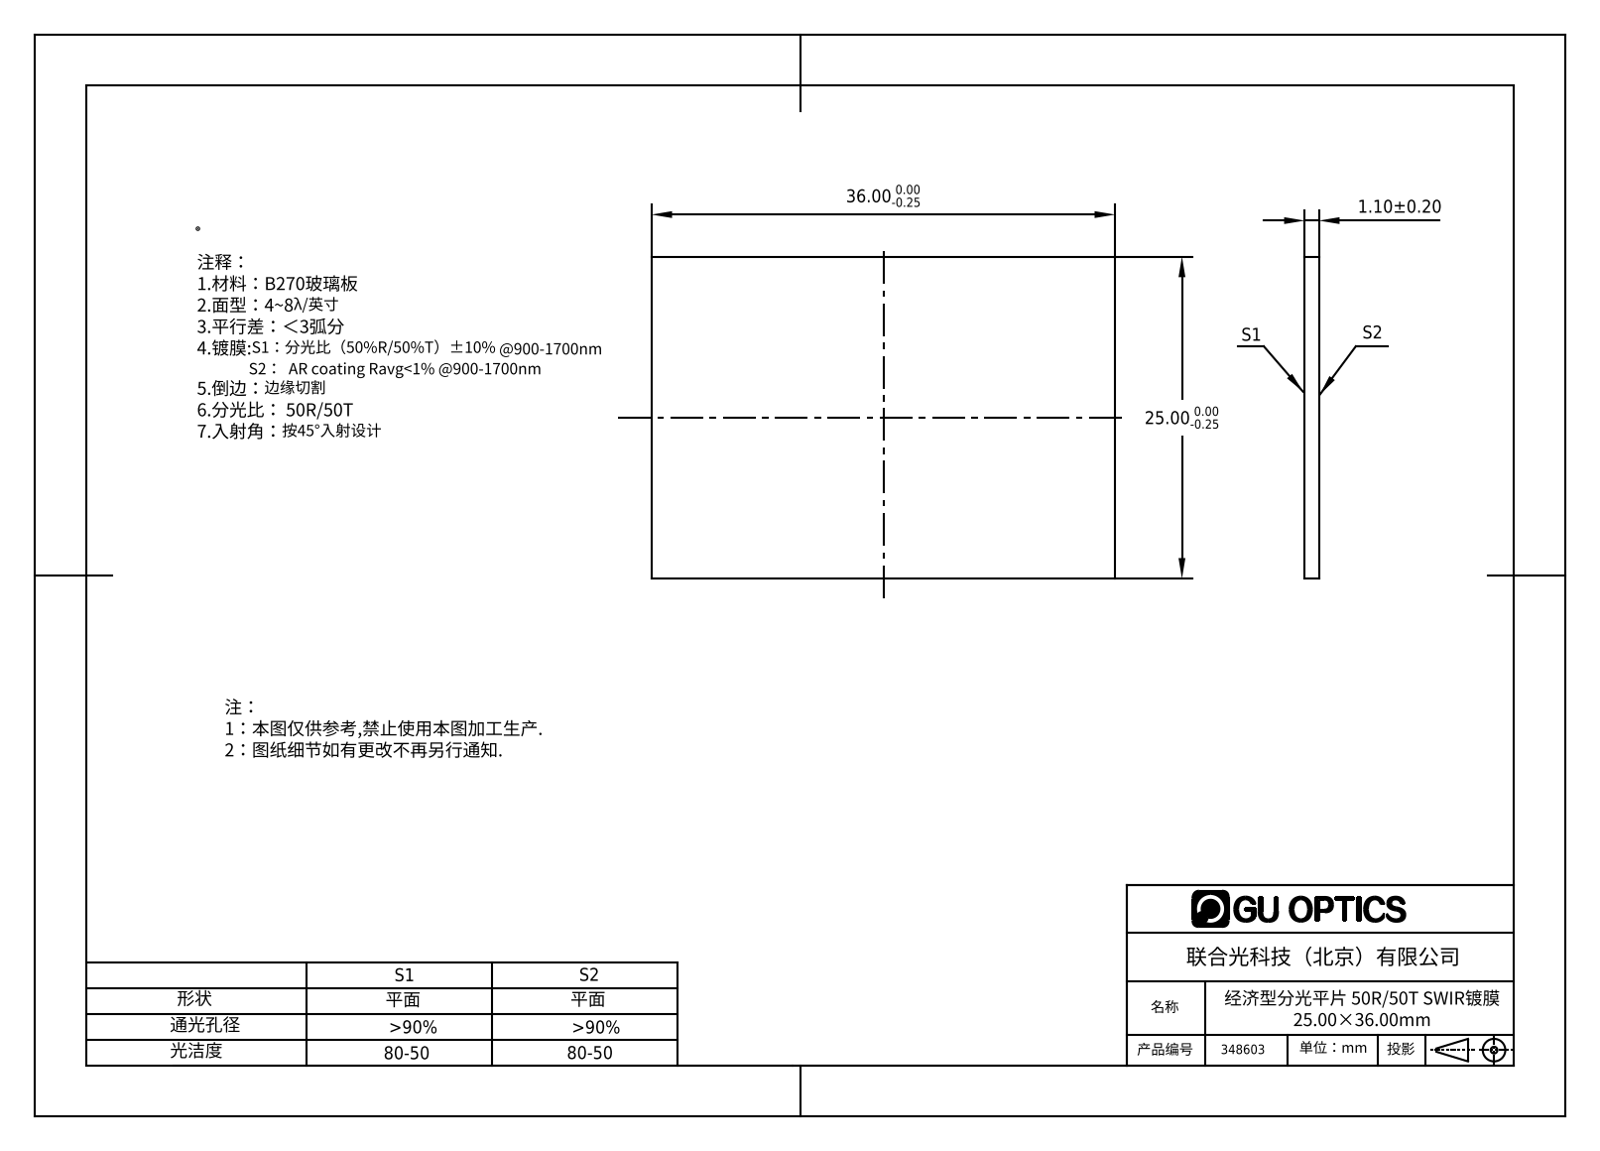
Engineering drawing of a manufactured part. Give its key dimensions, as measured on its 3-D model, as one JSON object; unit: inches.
{"part_name": "348505", "step_written_by": "SolidWorks 2016 (CONFIG_CONTROL_DESIGN)", "units": "inches", "bodies": {"solids": 1, "faces": 6, "planar": 6, "cylindrical": 0, "other": 0}, "overall_size": [1.417, 0.984, 0.043], "volume_in3": 0.06, "surface_area_in2": 2.998, "face_to_face_distances": [0.043, 0.984, 1.417]}
